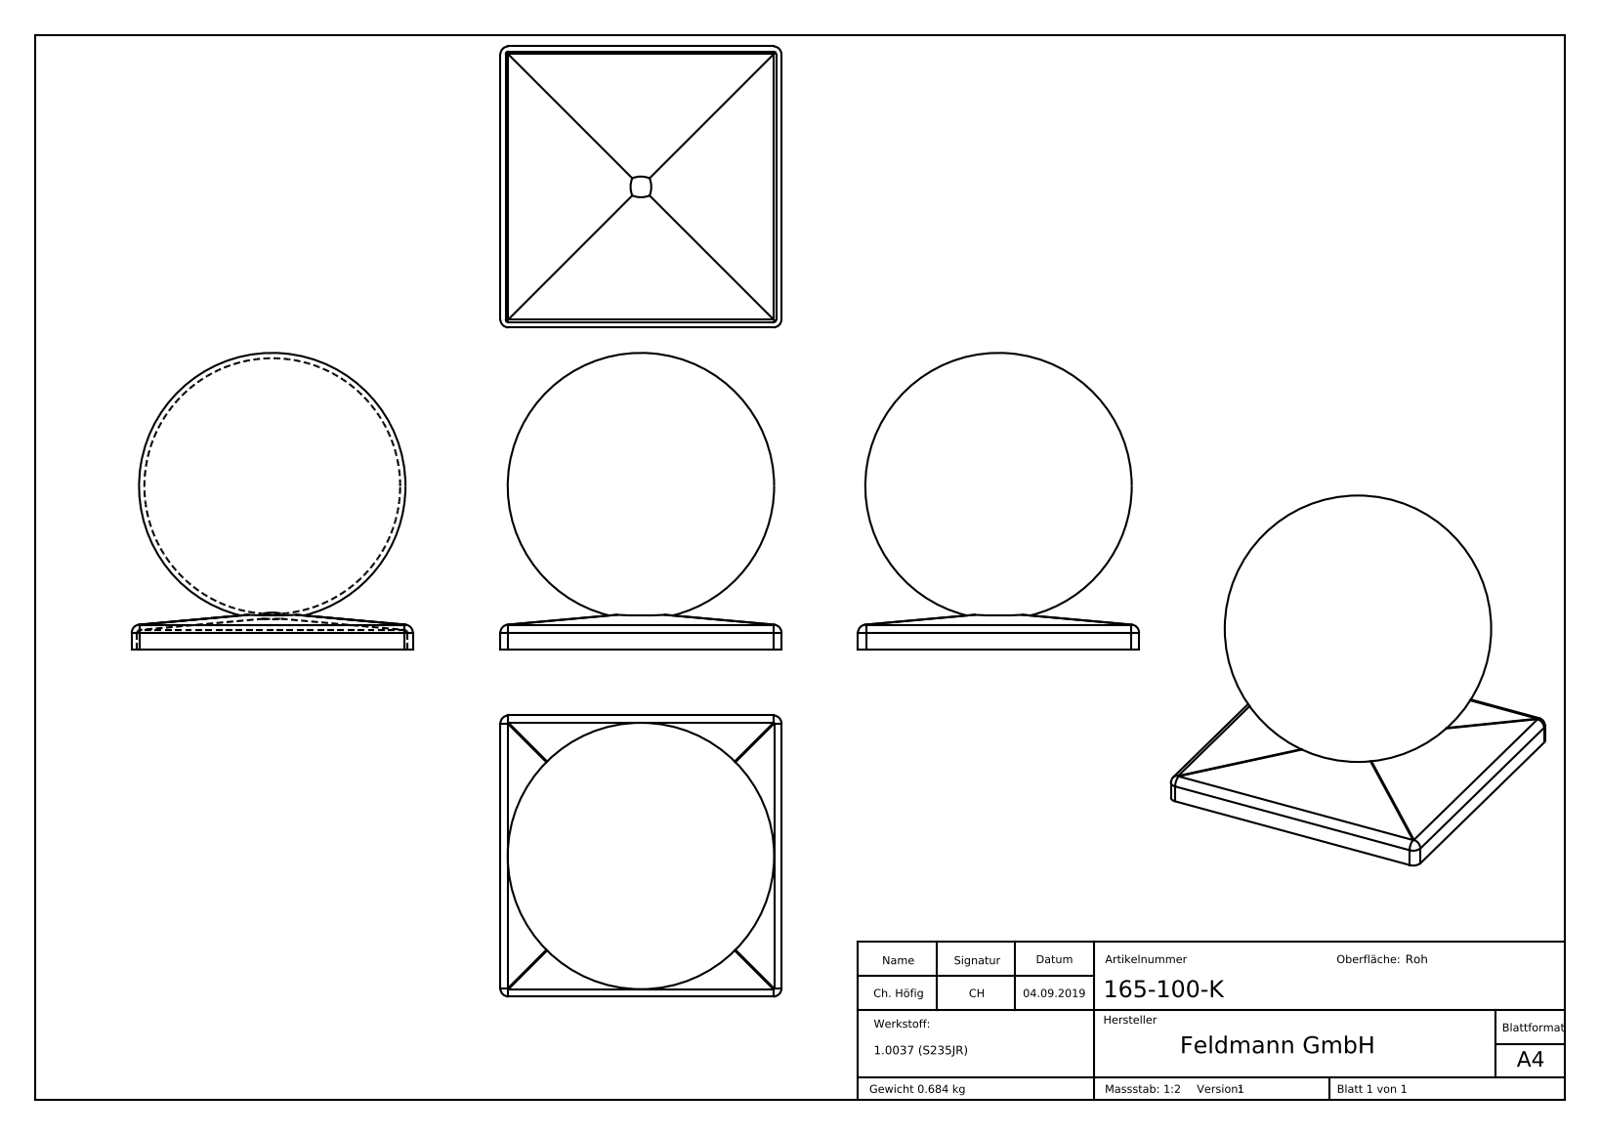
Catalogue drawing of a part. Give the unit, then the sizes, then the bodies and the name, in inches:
Units: inches
Overall size (bounding box): 4.39 × 4.154 × 4.154
Partial cylindrical surfaces — rounded edges, fillets, slot ends (radius × count): R0.118 ×12, R0.039 ×8
Main face-to-face distances: 0.079, 4.075, 4.154, 3.996, 0.075, 4, 4.079, 0.25, 0.039, 0.023
Volume: 5.348 in³ · Surface area: 136.5 in²
Bodies: 1 solid, 344 faces (174 planar, 24 cylindrical, 146 other)
Part name (STEP PRODUCT): 165-100-K
STEP written by: SolidWorks 2015 (CONFIG_CONTROL_DESIGN)
